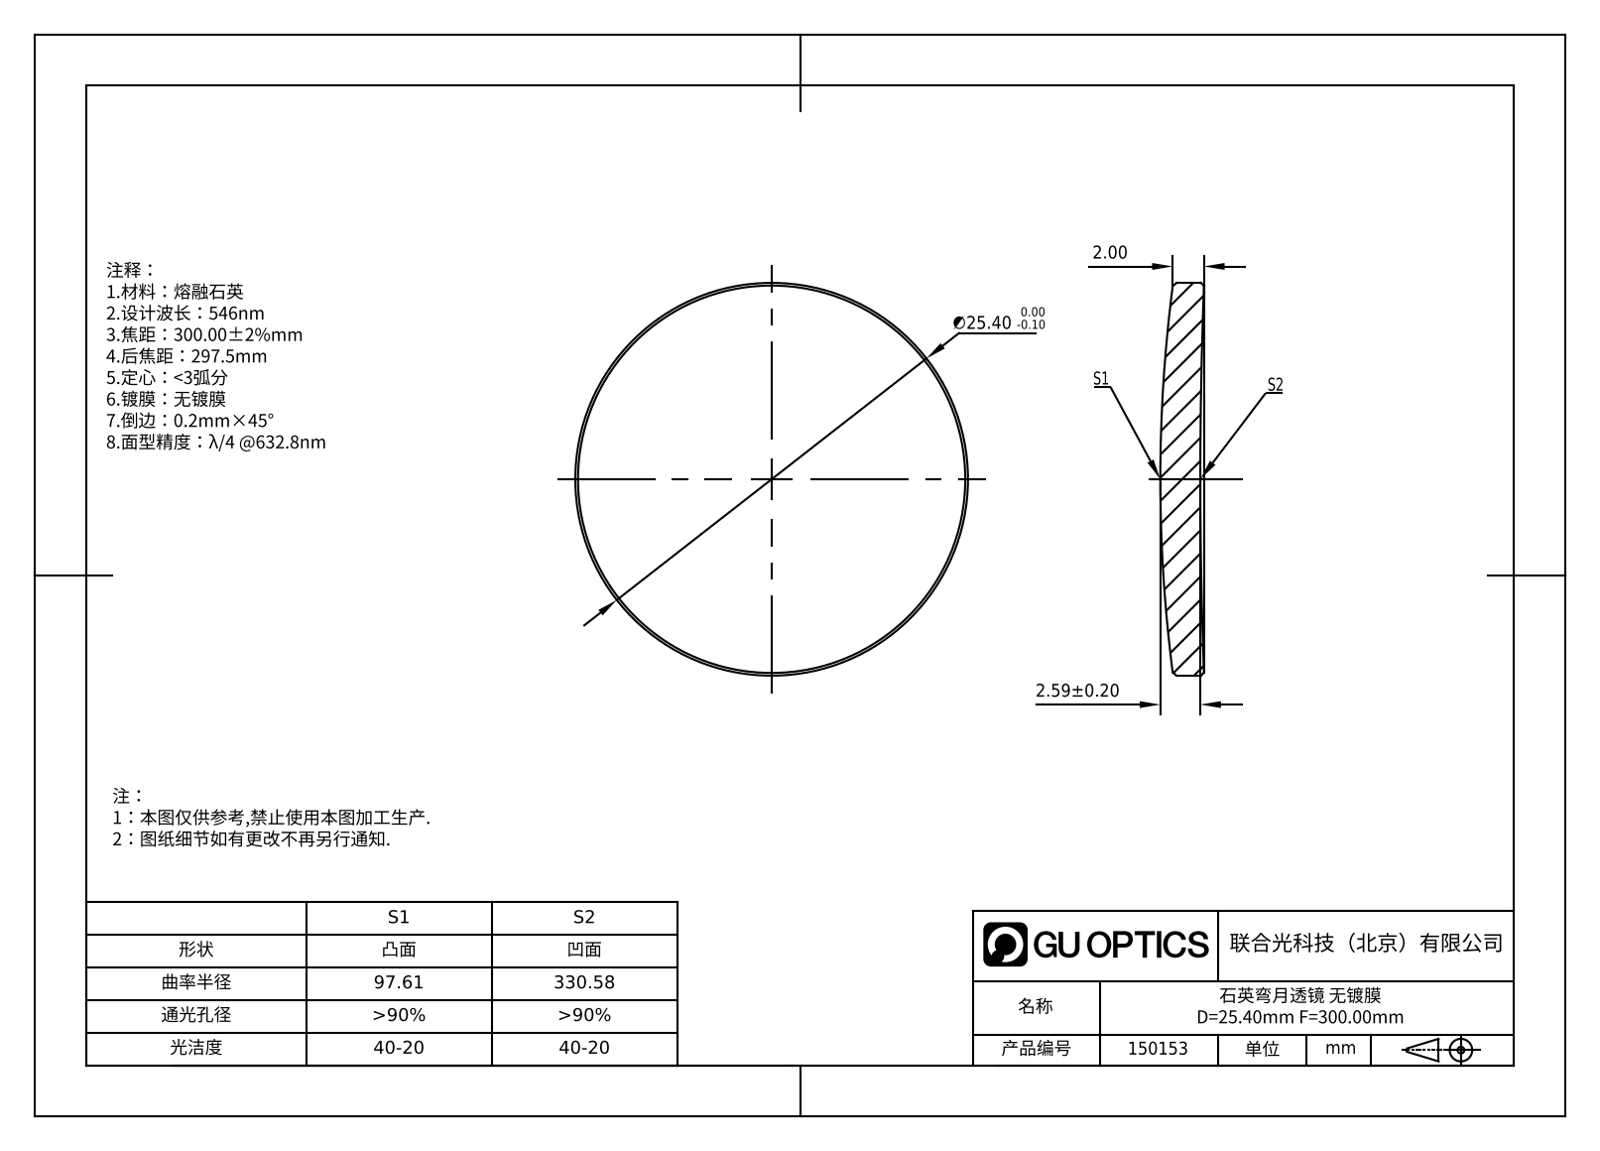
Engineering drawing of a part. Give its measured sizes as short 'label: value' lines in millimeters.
name: GLM2-025B-300
written by: SolidWorks 2022 (AUTOMOTIVE_DESIGN)
unit: mm
bodies: 1 solid, 10 faces (0 planar, 2 cylindrical, 8 other)
size: 25.4 × 25.4 × 2.82
volume: 1 159 mm³; area: 1 157 mm²
bosses: 1× ⌀25.4
